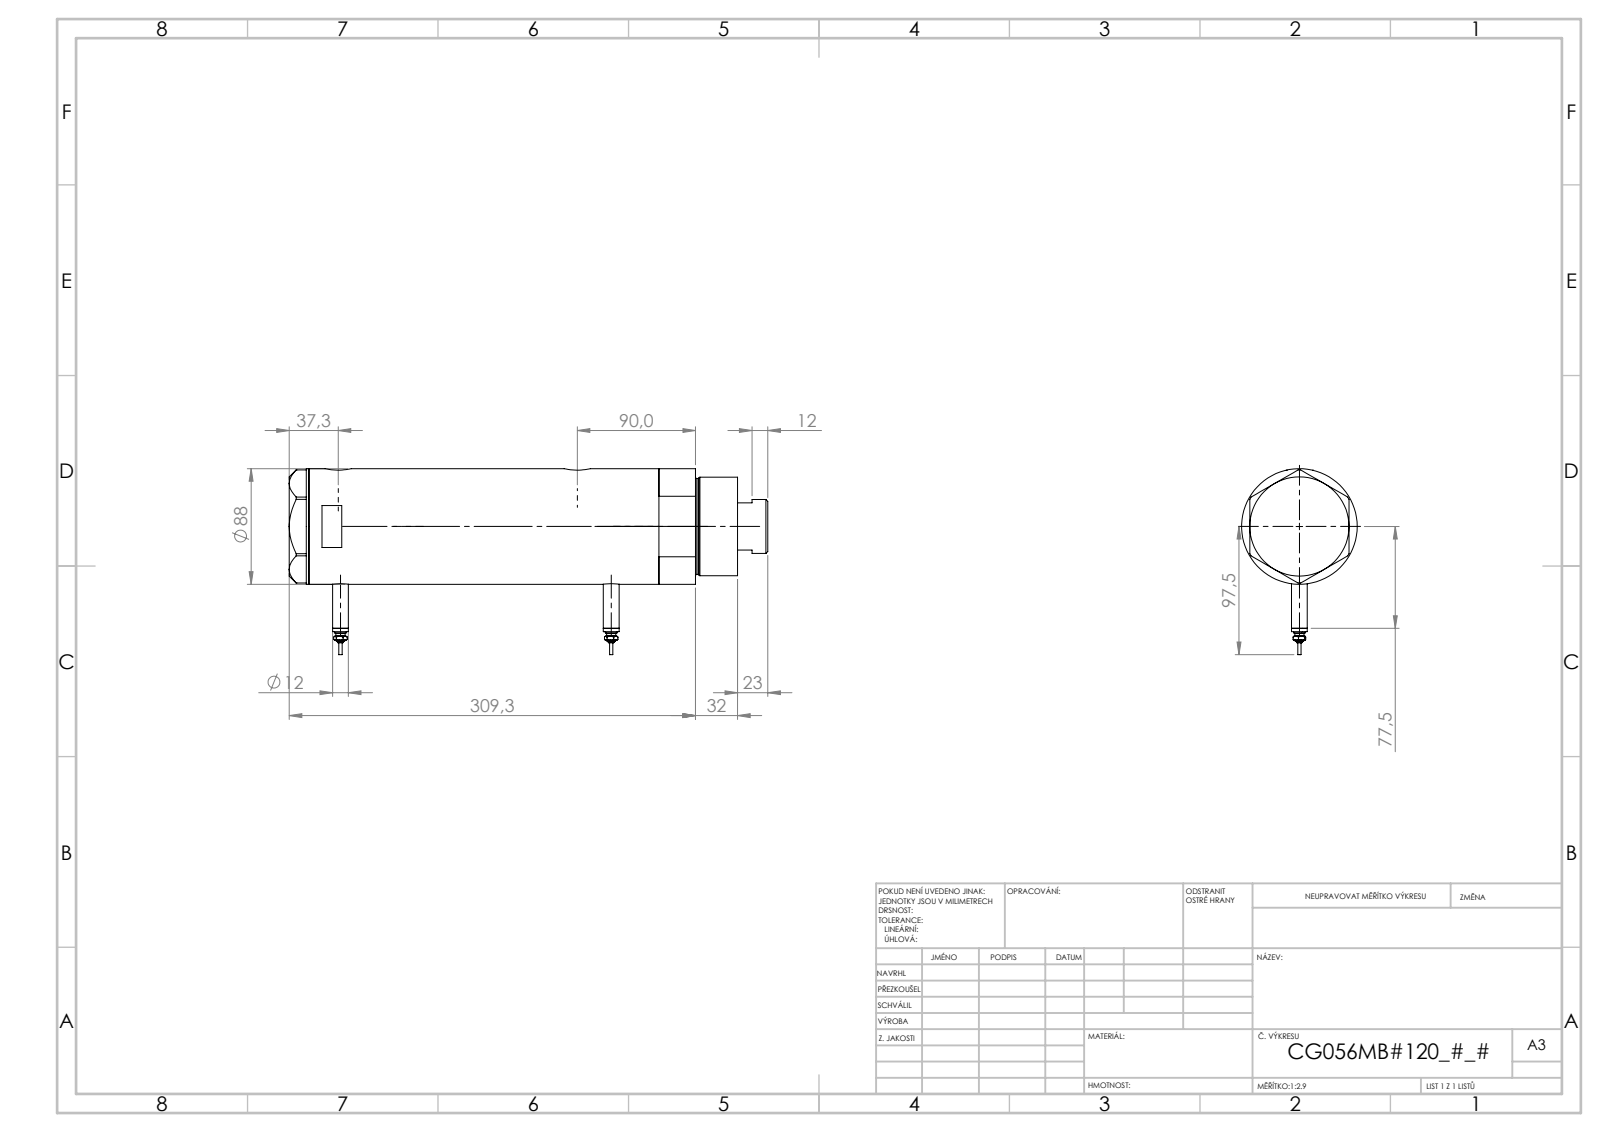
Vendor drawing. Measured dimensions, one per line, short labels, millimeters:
name: V270CG_MIDDLE; V270CG_VC; Switch; V270CG_BACK (+1 more)
written by: SolidWorks 2019 (CONFIG_CONTROL_DESIGN)
unit: mm
bodies: 6 solids, 213 faces (80 planar, 69 cylindrical, 64 other)
size: 364.3 × 141.5 × 88
volume: 1 891 000 mm³; area: 265 493 mm²
holes: 2× ⌀12.5, 2× ⌀13.16, 2× ⌀20, 1× ⌀14.5, 1× ⌀42, 1× ⌀43.5, 1× ⌀56, 1× ⌀60, 1× ⌀80
bosses: 2× ⌀12, 2× ⌀9, 2× ⌀7, 2× ⌀4.5, 2× ⌀2.5, 1× ⌀88, 1× ⌀75, 1× ⌀73
face distances: 204.4, 26, 178.4, 15, 41, 219.4, 326.3, 341.3, 300.3, 121.9
hole spacings: 1.7, 25.8, 180.3, 182, 206.1, 207.8
